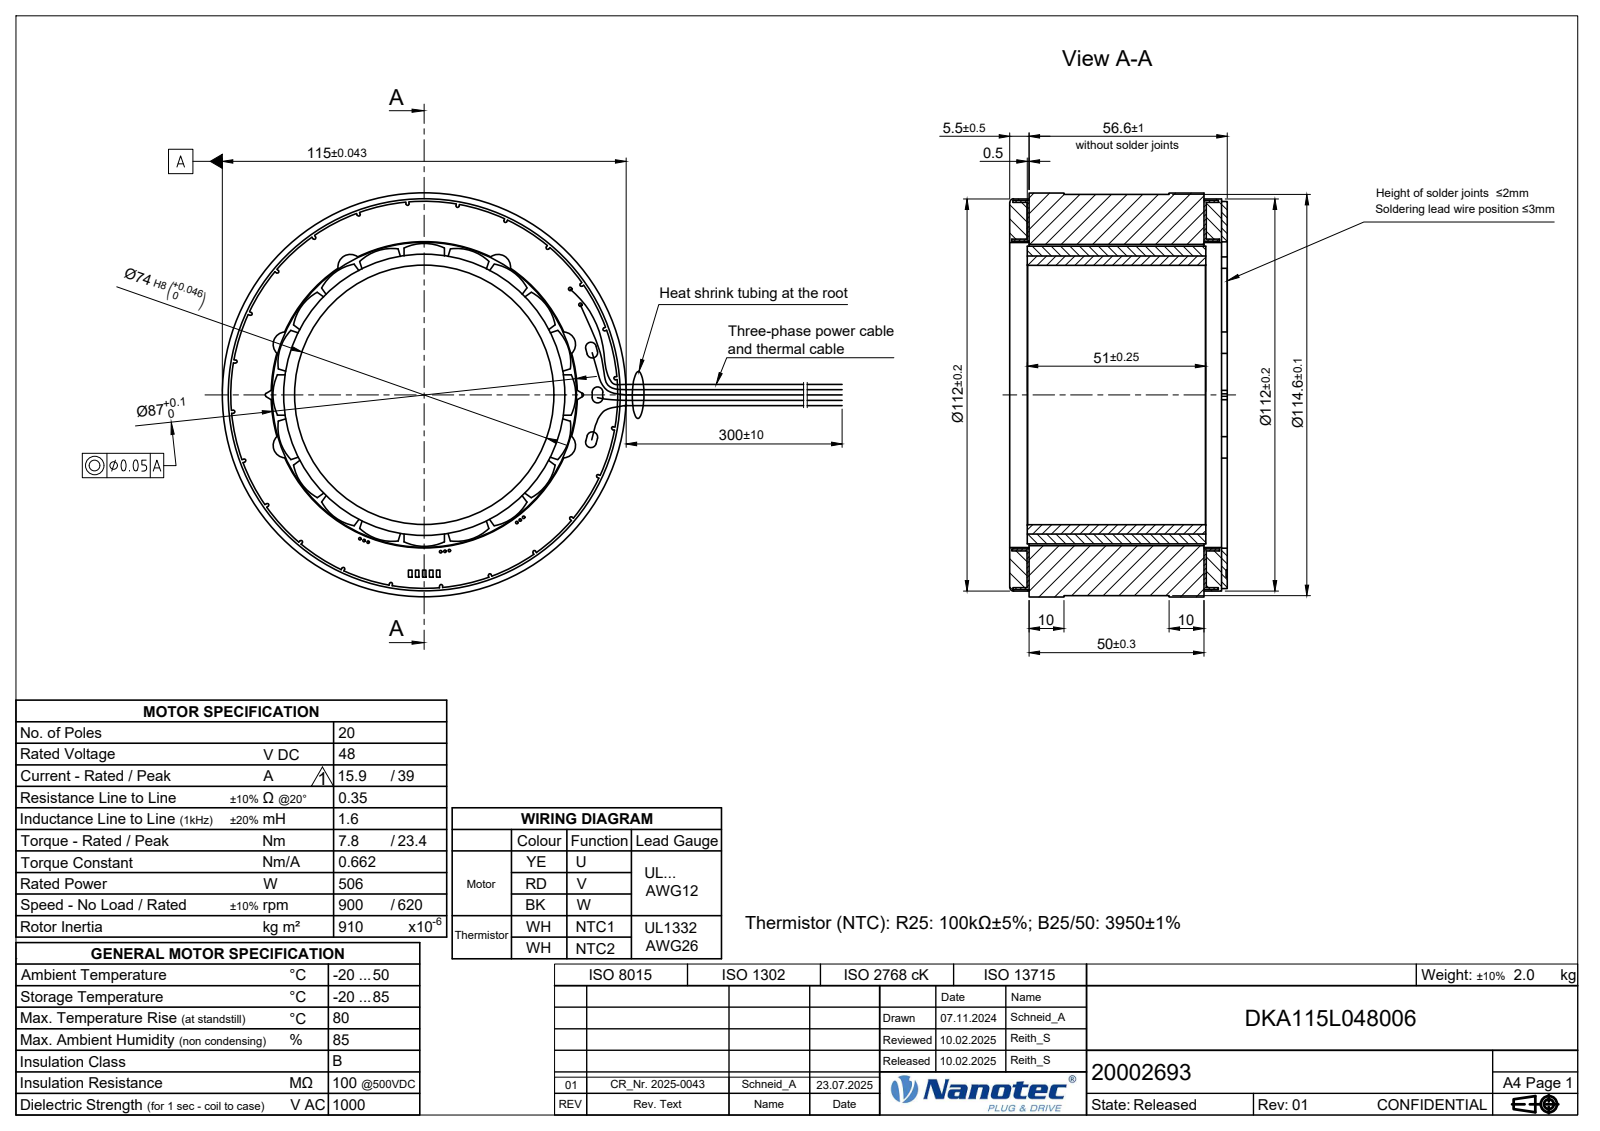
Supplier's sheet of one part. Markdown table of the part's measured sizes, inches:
| quantity | value |
| --- | --- |
| part name | 0001602239_SW0002 |
| STEP written by | CREO PARAMETRIC BY PTC INC, 2017110 (CONFIG_CONTROL_DESIGN) |
| units | inches |
| bodies | 2 solids, 241 faces (121 planar, 118 cylindrical, 2 other) |
| overall size | 4.539 × 4.539 × 2.445 |
| volume | 20.56 in³ |
| surface area | 119.9 in² |
| round holes (diameter × count) | 0.028 × 9, 0.315 × 3, 0.039 × 2, 2.913 × 1, 3.425 × 1, 3.445 × 1 |
| round bosses / shafts (diameter × count) | 4.539 × 1, 4.512 × 1, 4.409 × 1, 4.35 × 1, 3.346 × 1 |
| partial cylindrical surfaces (radius × count) | 0.018 × 24, 0.059 × 6, 0.14 × 6, 0.008 × 4, 0.02 × 2 |
| main face-to-face distances | 2.445, 0.197, 2.008, 2.205, 2.248, 0.24, 0.02, 1.988, 2.185, 0.26 |
| hole center spacings | 1.772, 0.049, 0.917, 0.098, 0.869, 0.965, 1.012, 1.929 |
